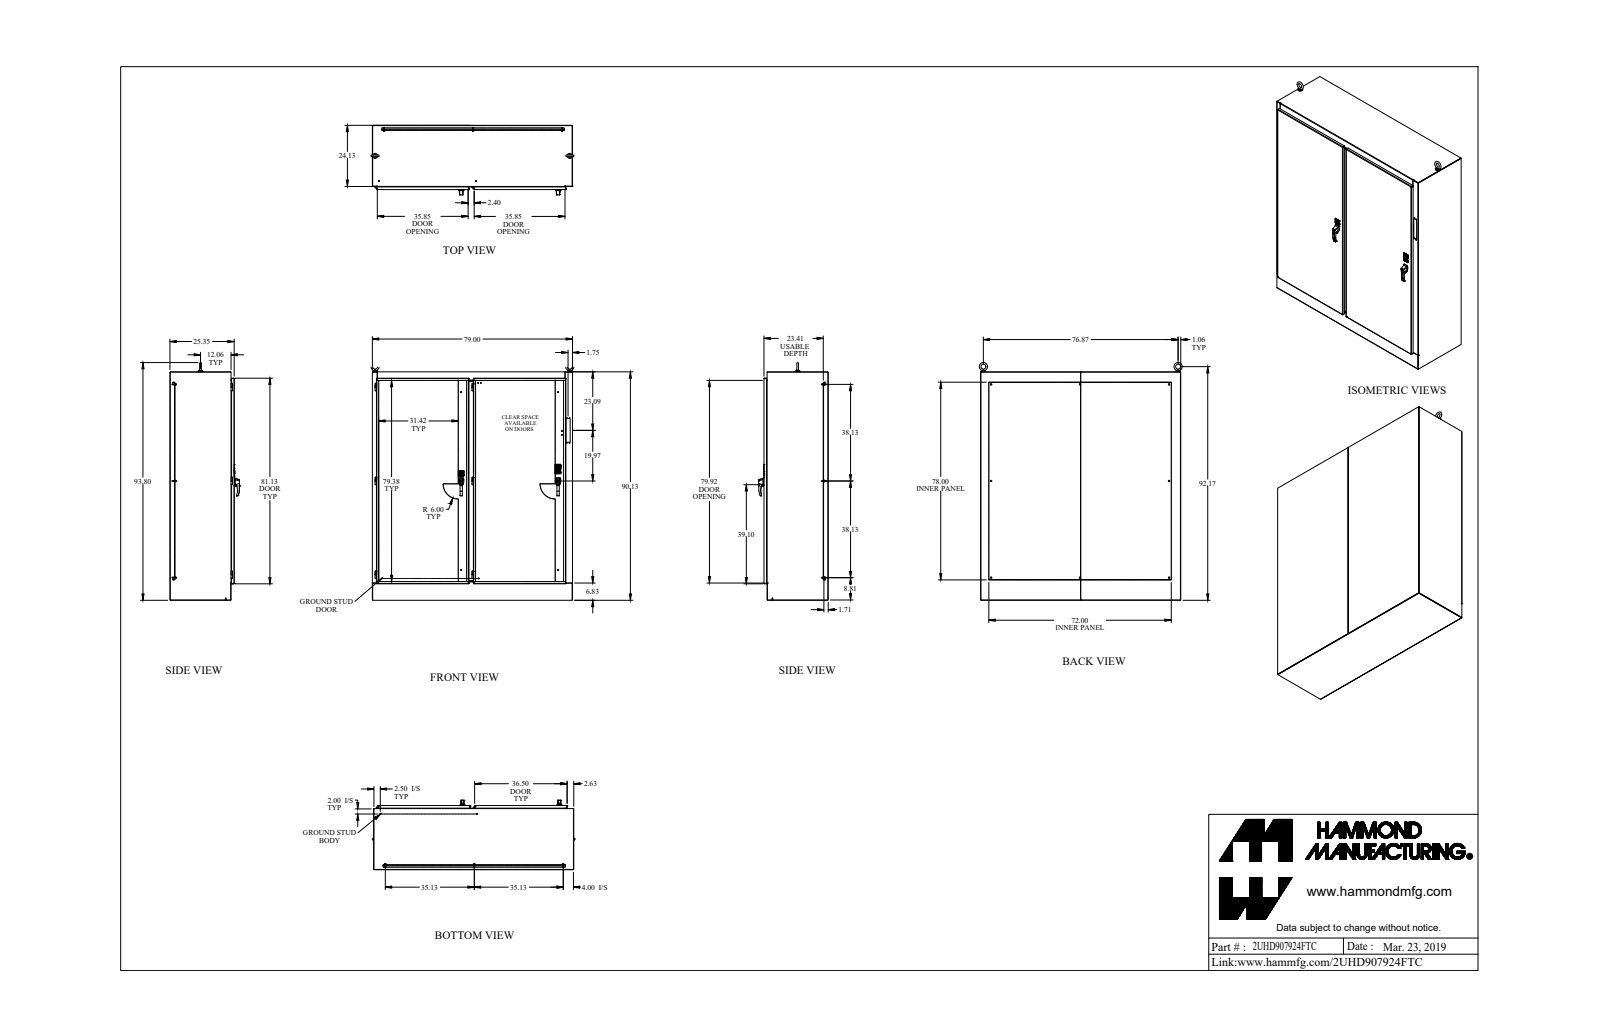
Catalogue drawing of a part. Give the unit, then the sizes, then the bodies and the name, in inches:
Units: inches
Overall size (bounding box): 93.799 × 80.122 × 27.466
Round holes (diameter × count): ⌀0.196 ×12, ⌀0.281 ×11, ⌀0.307 ×11, ⌀0.25 ×10, ⌀0.35 ×8, ⌀0.257 ×6, ⌀0.313 ×6, ⌀0.445 ×5, ⌀0.28 ×4, ⌀0.282 ×4, ⌀0.375 ×4, ⌀0.39 ×4
Round bosses / shafts (diameter × count): ⌀0.25 ×19, ⌀1 ×14, ⌀0.65 ×9, ⌀0.375 ×9, ⌀0.33 ×9, ⌀0.625 ×8, ⌀0.281 ×8, ⌀0.75 ×6
Partial cylindrical surfaces — rounded edges, fillets, slot ends (radius × count): R0.125 ×62, R0.06 ×53, R0.5 ×38, R0.185 ×32, R0.03 ×28, R0.017 ×16, R0.018 ×16, R0.032 ×12
Main face-to-face distances: 0.125, 0.072, 23.431, 0.125, 25.369, 25.243, 1.937, 1.812, 1.865, 1.74
Hole centre spacings: 38.249, 1, 2, 1.126, 1.287, 33.937, 35.063, 35.068
Volume: 6 161 in³ · Surface area: 65 223 in²
Bodies: 216 solids, 3241 faces (1842 planar, 923 cylindrical, 476 other)
Part name (STEP PRODUCT): 2UHD907924FTC
STEP written by: SolidWorks 2018 (AUTOMOTIVE_DESIGN)
